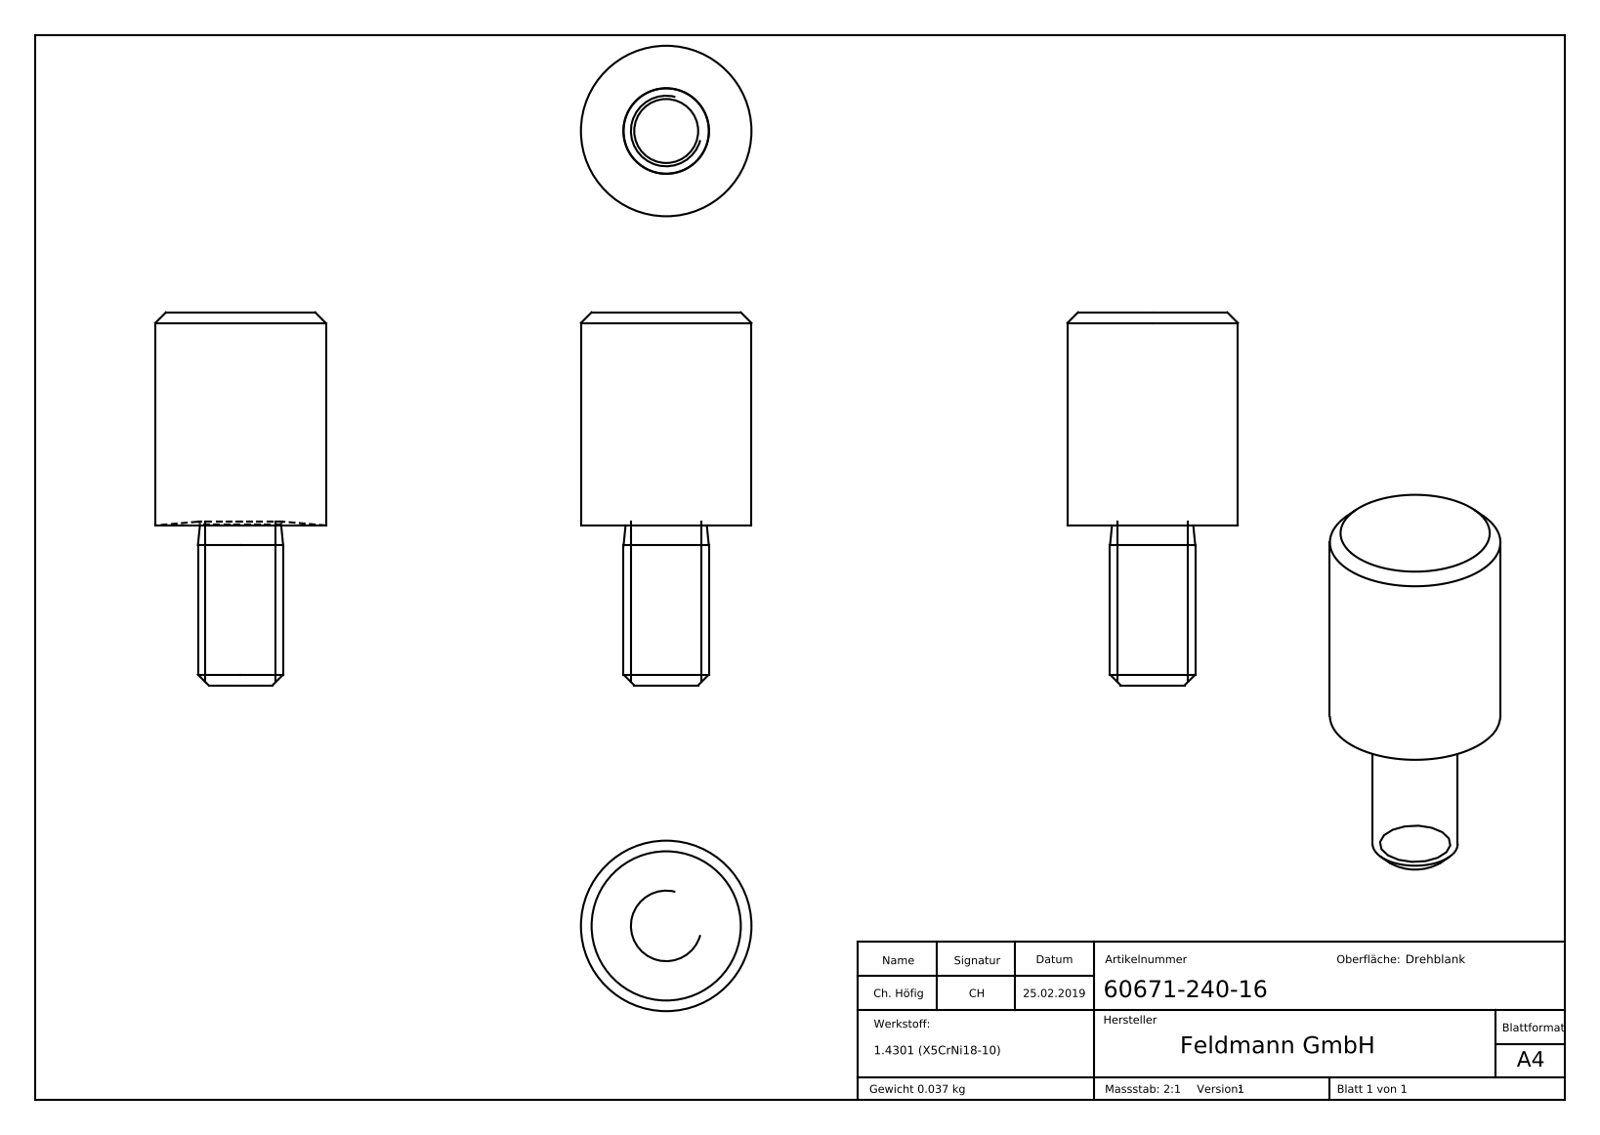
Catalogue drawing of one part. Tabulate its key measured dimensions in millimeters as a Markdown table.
| quantity | value |
| --- | --- |
| part name | 60671-240-16 |
| STEP written by | SolidWorks 2015 (CONFIG_CONTROL_DESIGN) |
| units | millimeters |
| bodies | 1 solid, 254 faces (139 planar, 4 cylindrical, 111 other) |
| overall size | 35 × 16 × 16 |
| volume | 4 710 mm³ |
| surface area | 1 751 mm² |
| round bosses / shafts (diameter × count) | 16 × 1, 8 × 1 |
| main face-to-face distances | 35, 34.9, 0.65, 0.92, 1.44, 0.57, 1.3, 0.33, 1.68, 0.35 |
